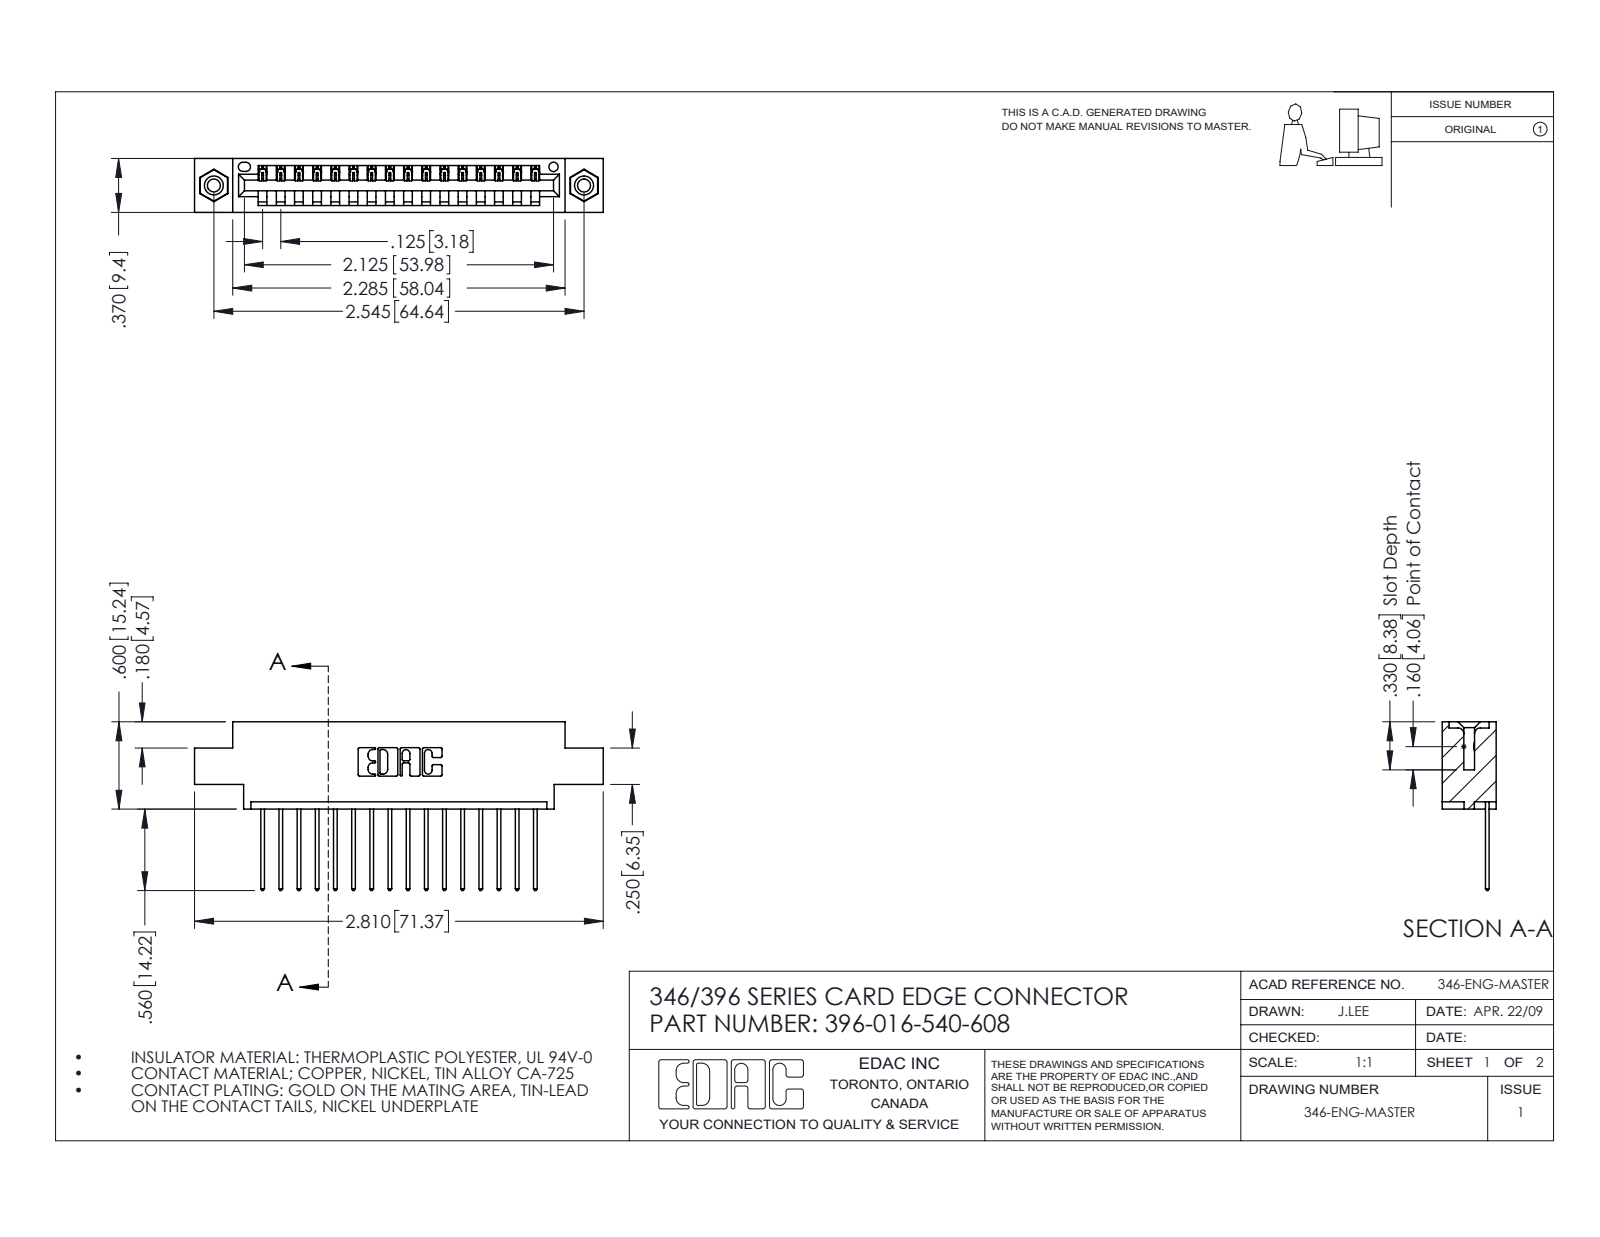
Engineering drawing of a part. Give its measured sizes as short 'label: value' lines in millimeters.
name: 345-250-001_345-250-003-102; 396-016-540-608; 346 Part_0.170 Offset - 0.156 Dia-TI; 345-292-001_345-293-140
written by: SolidWorks 2016 (CONFIG_CONTROL_DESIGN)
unit: mm
bodies: 19 solids, 1114 faces (752 planar, 346 cylindrical, 16 other)
size: 71.4 × 29.5 × 9.4
volume: 6 510 mm³; area: 8 200 mm²
holes: 2× ⌀2.3, 2× ⌀3.2, 2× ⌀4, 1× ⌀1.6
bosses: 2× ⌀3.9
rounds: 32× R0.2, 32× R0.3, 22× R0.3, 6× R0.2, 6× R0.8, 3× R0.7, 2× R0.8, 2× R1
face distances: 1.2, 8.2, 9.4, 6.4, 1.8, 7.6, 0.6, 5.6, 3.8, 2.5
hole spacings: 6.2, 59.4, 64.6
